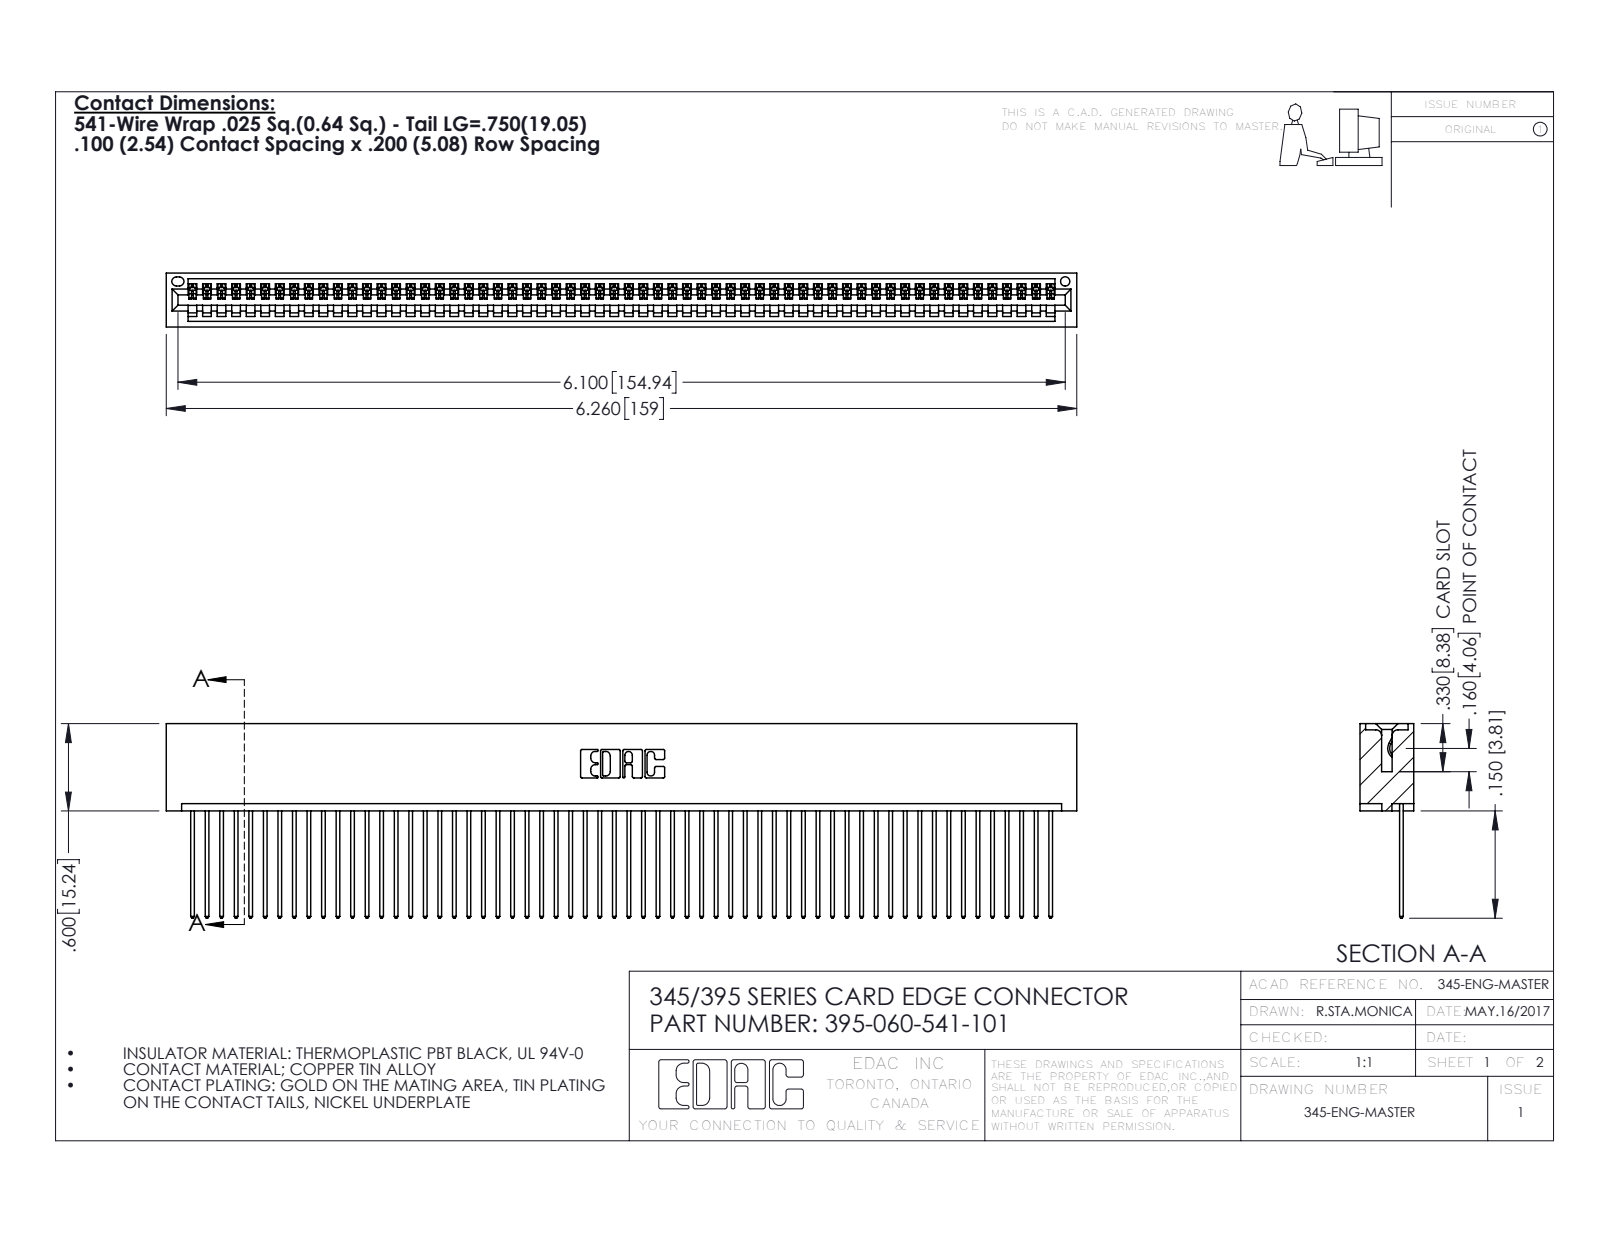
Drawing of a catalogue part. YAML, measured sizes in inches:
part_name: "345 Part_No Mounting Lugs; 395-060-541-101; 345-292-001_345-293-141"
step_written_by: "SolidWorks 2016 (CONFIG_CONTROL_DESIGN)"
units: inches
bodies: {solids: 61, faces: 3598, planar: 2476, cylindrical: 1122, other: 0}
overall_size: [6.26, 1.337, 0.37]
volume: 0.978
surface_area: 35.5
round_holes:
  - {diameter: 0.064, count: 1}
partial_cylinders:
  - {radius: 0.006, count: 120}
  - {radius: 0.01, count: 120}
  - {radius: 0.01, count: 22}
  - {radius: 0.007, count: 6}
  - {radius: 0.031, count: 6}
  - {radius: 0.026, count: 3}
  - {radius: 0.031, count: 2}
  - {radius: 0.04, count: 2}
face_to_face_distances: [0.072, 0.298, 0.098, 0.272, 0.025, 0.37, 0.2, 0.225, 0.149, 0.072]
